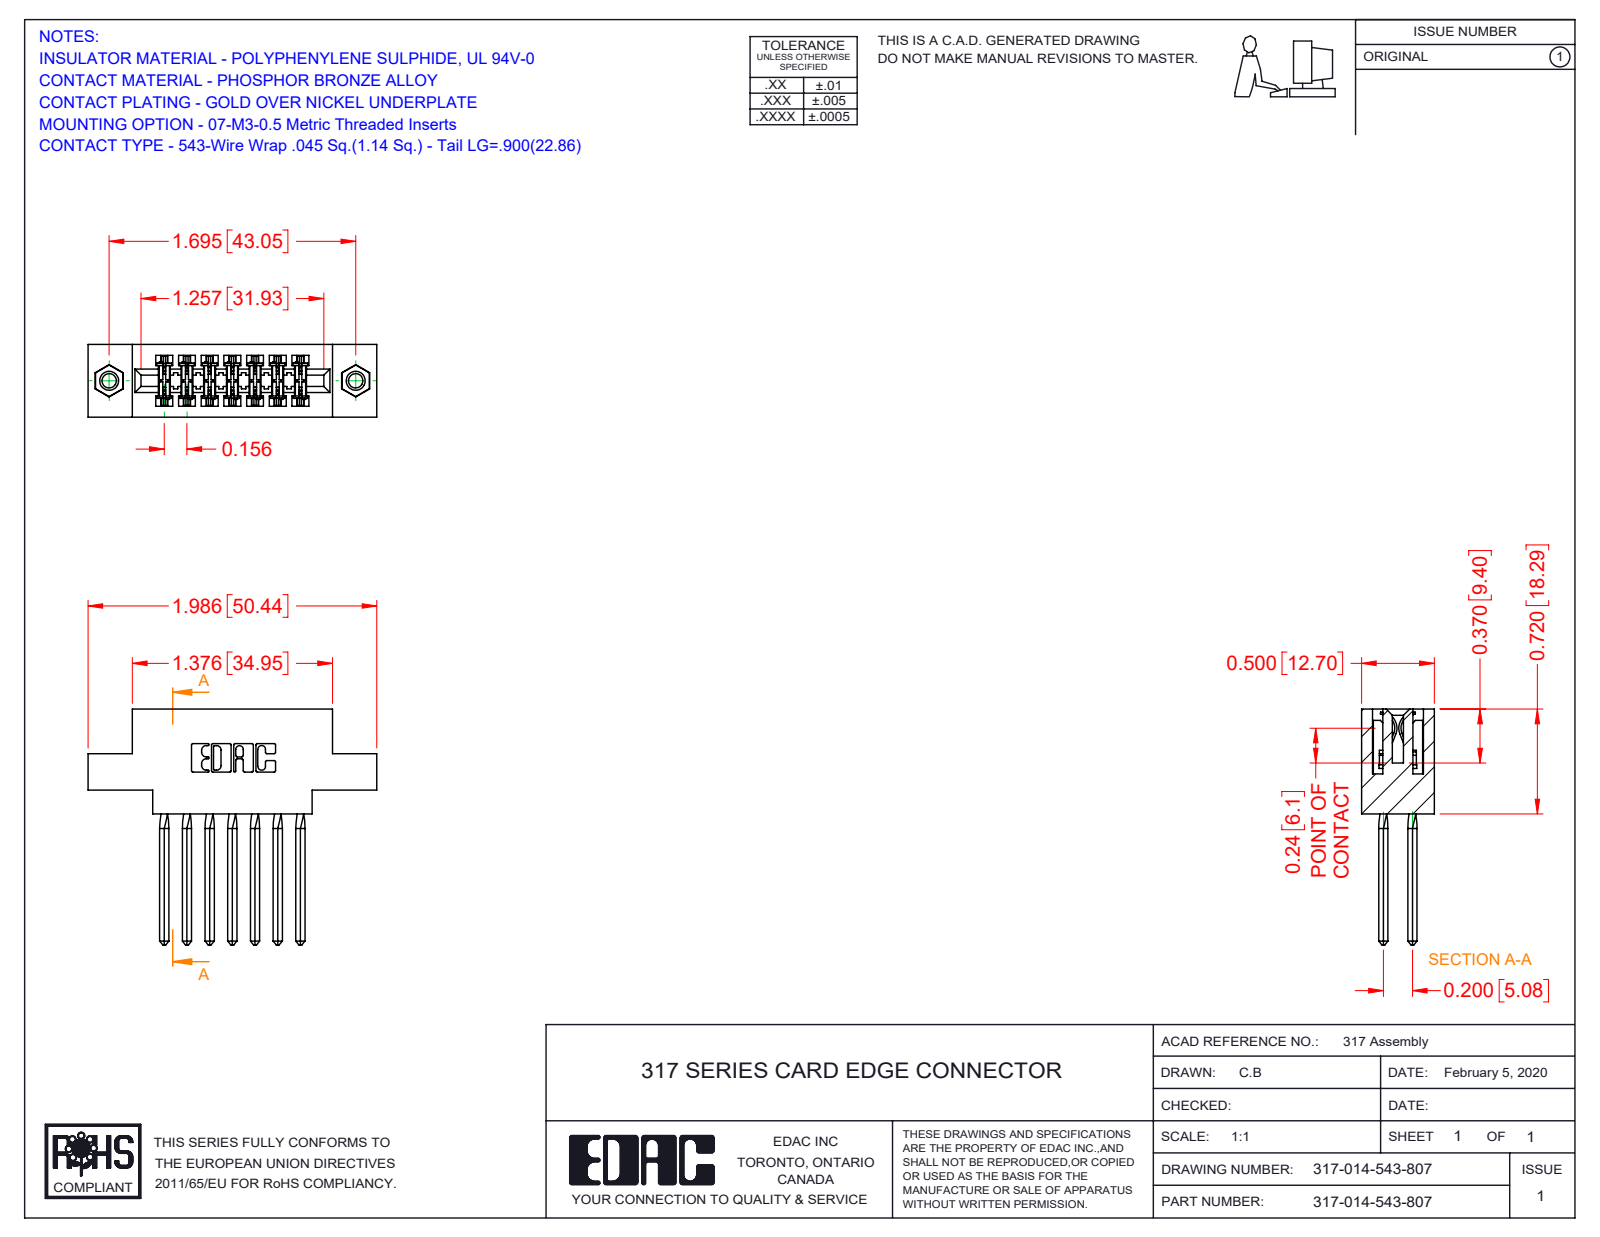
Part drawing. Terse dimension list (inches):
name: 317-290-001_543; 345-250-001_345-250-005-103; 317 Part_.156 Dia - TI; 317-014-543-807
written by: SolidWorks 2016 (CONFIG_CONTROL_DESIGN)
unit: in
bodies: 17 solids, 1408 faces (1112 planar, 224 cylindrical, 72 other)
size: 1.986 × 1.62 × 0.5
volume: 0.448 in³; area: 15.18 in²
holes: 2× ⌀0.098, 2× ⌀0.125, 2× ⌀0.156
bosses: 2× ⌀0.155
rounds: 28× R0.015, 22× R0.01, 6× R0.007, 6× R0.031, 3× R0.026, 2× R0.095, 2× R0.1, 2× R0.11
face distances: 0.11, 0.5, 0.075, 0.425, 0.22, 0.156, 0.116, 0.065, 0.331, 0.136
hole spacings: 1.695
